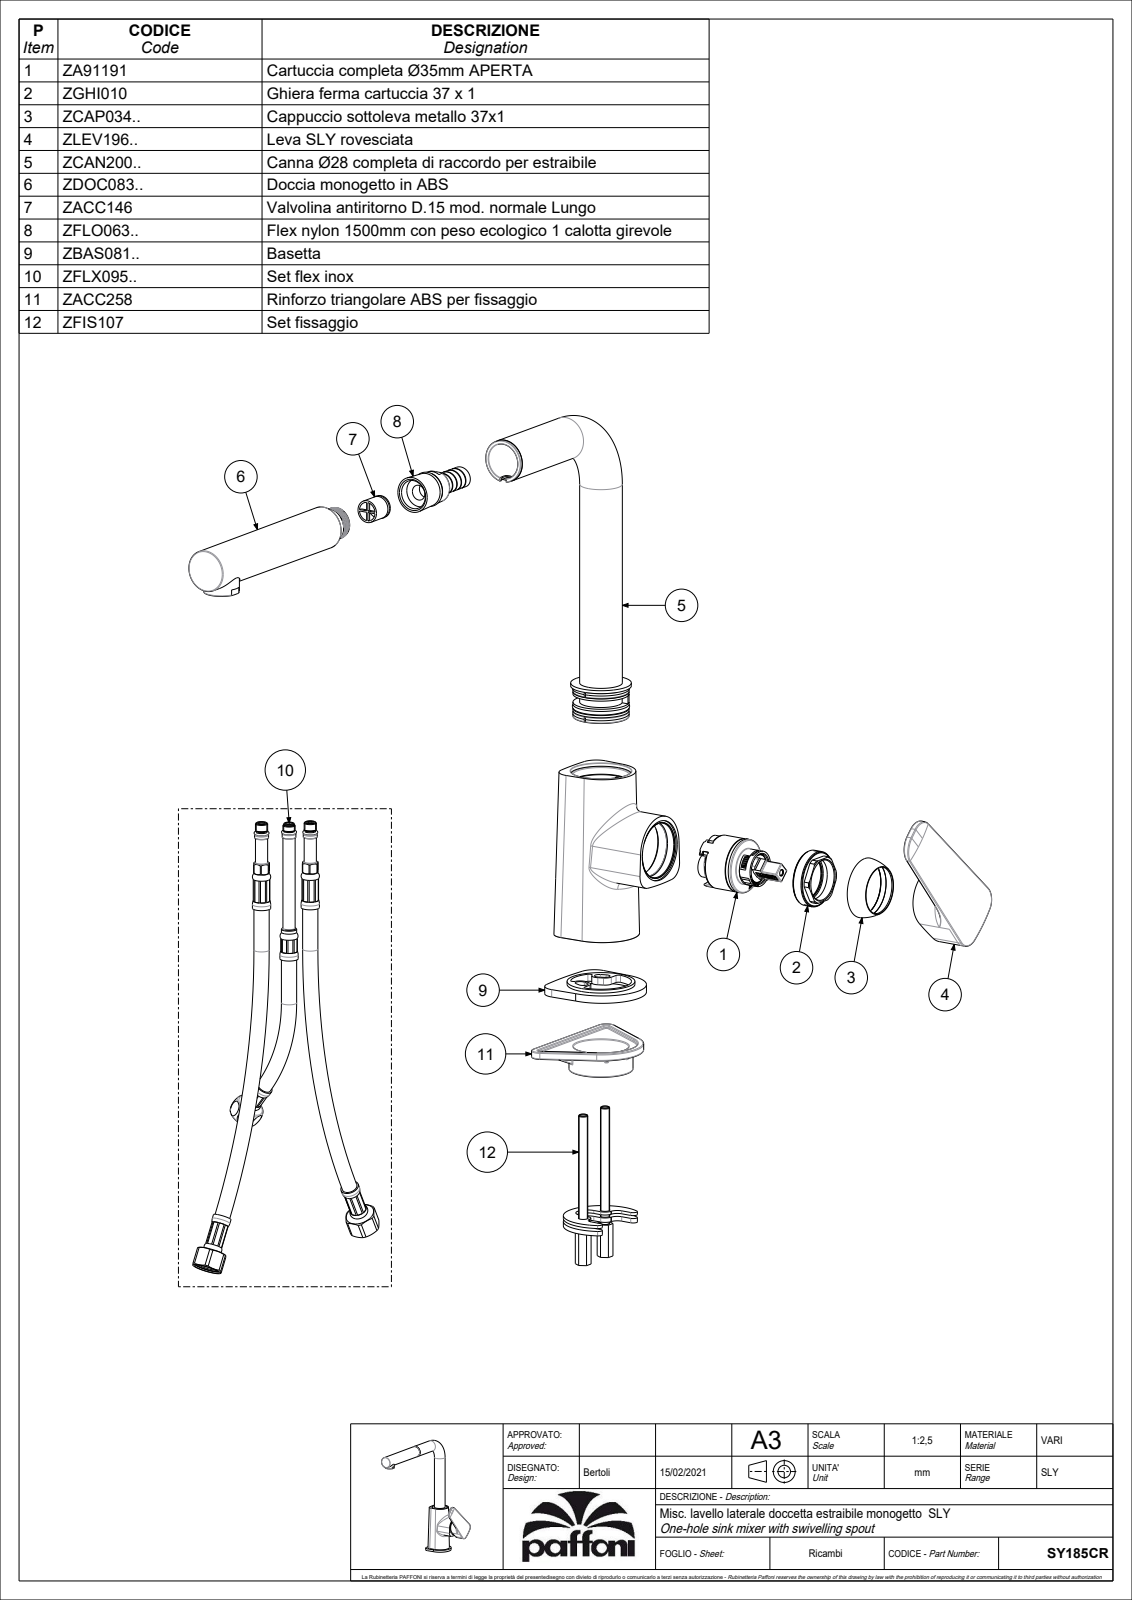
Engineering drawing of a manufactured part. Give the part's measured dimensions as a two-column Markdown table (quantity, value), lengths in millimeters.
| quantity | value |
| --- | --- |
| part name | SY185CR |
| STEP written by | CREO PARAMETRIC BY PTC INC, 2020044 (CONFIG_CONTROL_DESIGN) |
| units | millimeters |
| bodies | 2 solids, 4434 faces (2085 planar, 1756 cylindrical, 593 other) |
| overall size | 304.6 × 276.64 × 108.92 |
| volume | 306 883 mm³ |
| surface area | 190 462 mm² |
| round holes (diameter × count) | 0.4 × 480, 7 × 6, 5.5 × 3, 8.6 × 3, 9.4 × 3, 5 × 2, 8 × 2, 8.5 × 2, 25 × 2, 38 × 2, 40 × 2, 3 × 1 |
| round bosses / shafts (diameter × count) | 28 × 2, 23.5 × 2, 18 × 2, 4.8 × 2, 4 × 2, 44.5 × 1, 39.8 × 1, 36.8 × 1 |
| partial cylindrical surfaces (radius × count) | 0.2 × 60, 0.5 × 48, 1.5 × 13, 3 × 12, 1 × 11, 1.7 × 6, 5 × 6, 0.3 × 5 |
| main face-to-face distances | 2, 1.5, 5.5, 5, 7, 2.2, 2.8, 9.8, 7.5, 112.8 |
| hole center spacings | 10.48, 7.41, 1.34, 4.69, 6.63, 9.49, 11.38, 13.25 |
